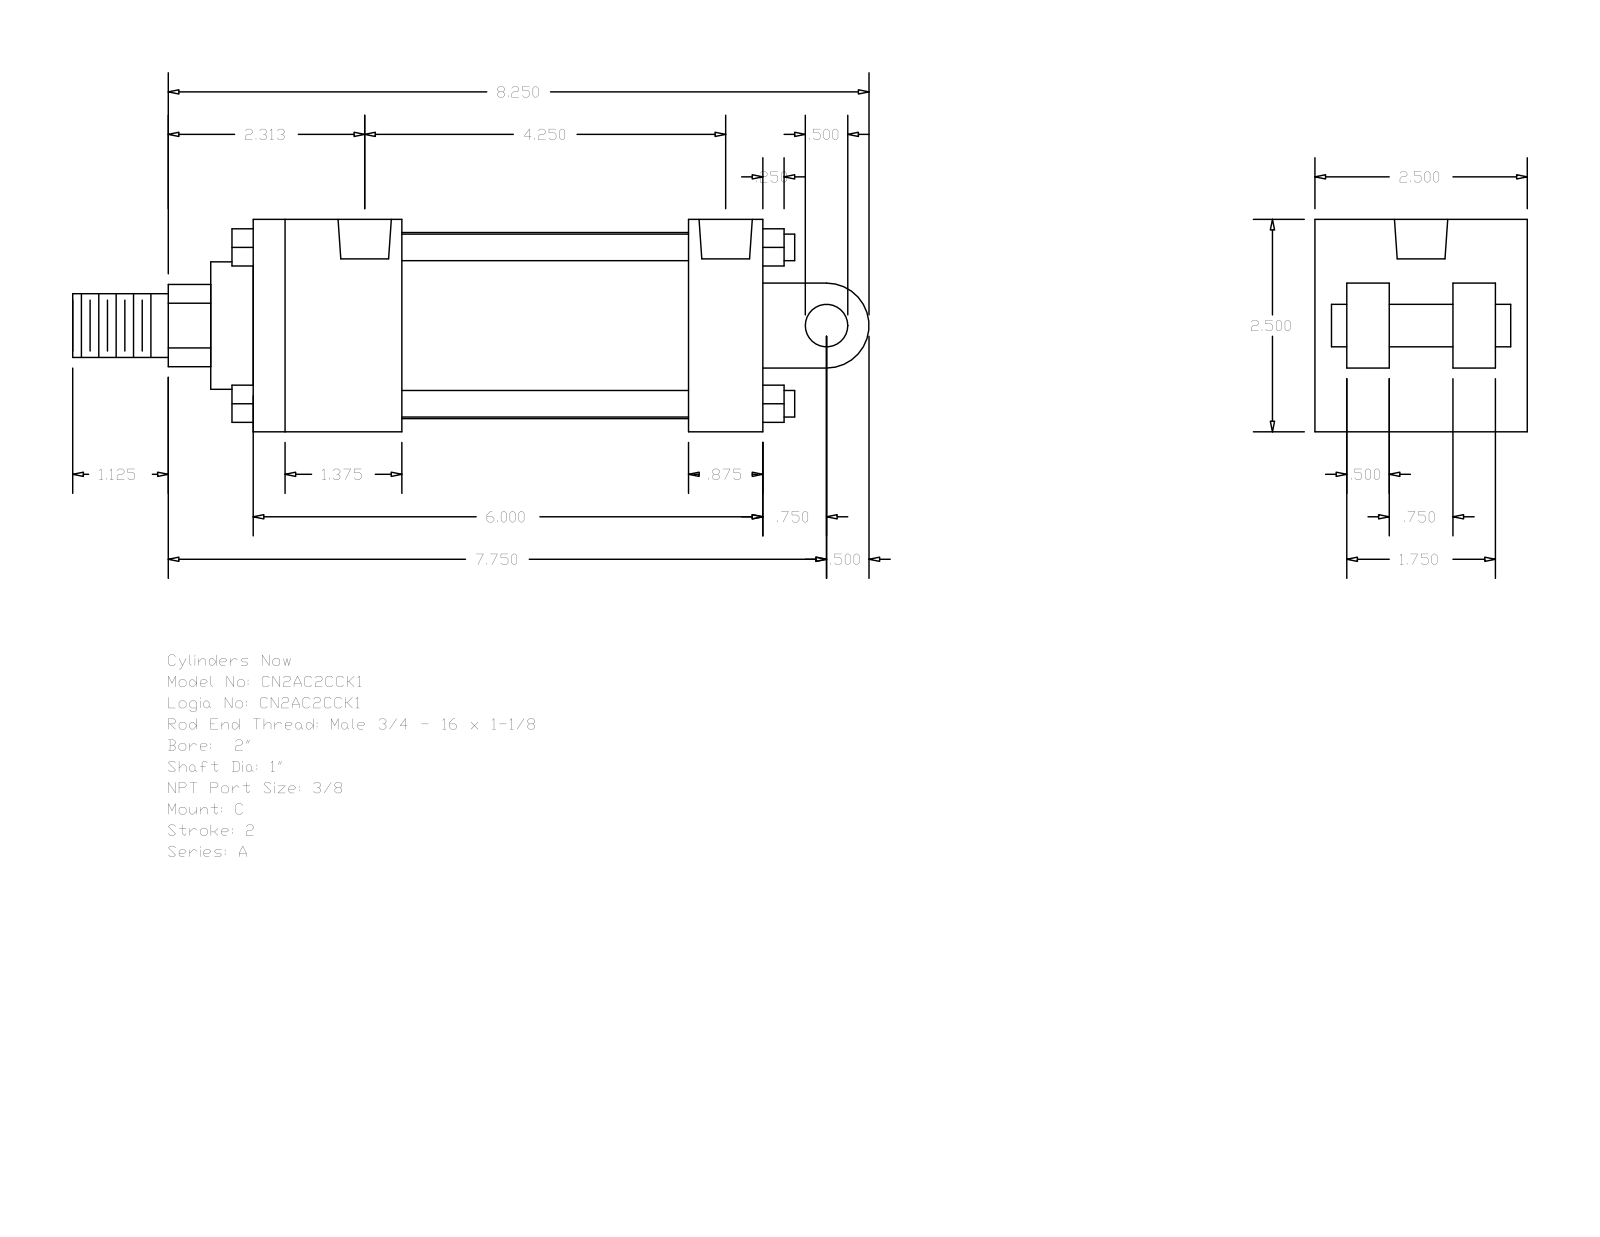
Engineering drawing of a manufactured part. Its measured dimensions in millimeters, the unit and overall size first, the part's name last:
Units: millimetres
Overall size (bounding box): 238.12 × 63.5 × 63.5
Round holes (diameter × count): ⌀5.56 ×4, ⌀15.93 ×2
Round bosses / shafts (diameter × count): ⌀7.94 ×4, ⌀55.63 ×1, ⌀38.1 ×1, ⌀25.4 ×1, ⌀19.05 ×1, ⌀12.7 ×1
Partial cylindrical surfaces — rounded edges, fillets, slot ends (radius × count): R12.29 ×1, R12.7 ×1
Main face-to-face distances: 63.5, 152.4, 44.45, 12.7, 9.52, 107.95, 130.17, 85.72, 22.23, 22.22
Hole centre spacings: 102.38, 1.59, 3.98, 103.97, 106.36, 107.95
Bodies: 0 solids, 135 faces (102 planar, 33 cylindrical, 0 other)
Part name (STEP PRODUCT): A_C__0200_1
STEP written by: GSSL Pune (CONFIG_CONTROL_DESIGN)
